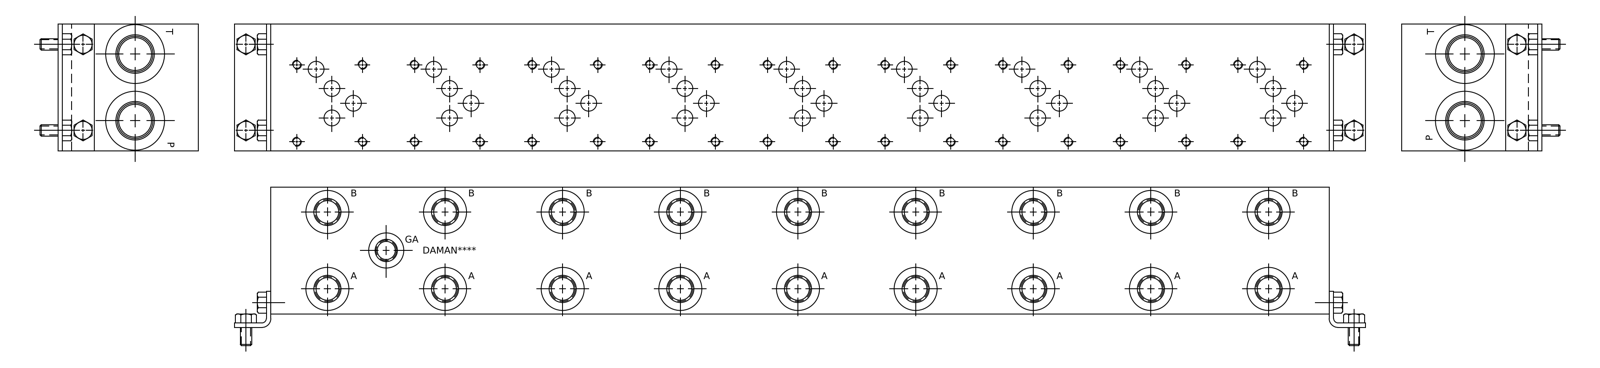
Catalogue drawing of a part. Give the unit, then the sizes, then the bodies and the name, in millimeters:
Units: millimetres
Overall size (bounding box): 742.95 × 88.9 × 88.9
Round holes (diameter × count): ⌀5.11 ×36, ⌀6.35 ×36, ⌀11.13 ×36, ⌀15.88 ×18, ⌀17.5 ×18, ⌀19.05 ×18, ⌀19.25 ×18, ⌀30.63 ×18, ⌀6.53 ×2, ⌀7.92 ×2, ⌀23.01 ×2, ⌀24.92 ×2
Main face-to-face distances: 88.9, 0.79, 88.11, 742.95, 742.16, 741.37, 15.06, 14.27, 73.84, 19.05
Hole centre spacings: 82.55, 165.1, 247.65, 253.46, 98.63, 330.2, 334.58, 173.7
Volume: 5 630 000 mm³ · Surface area: 338 766 mm²
Bodies: 1 solid, 1257 faces (587 planar, 231 cylindrical, 439 other)
Part name (STEP PRODUCT): Part_AD05P093S_3D
STEP written by: Autodesk Inventor 2019 (AUTOMOTIVE_DESIGN)
